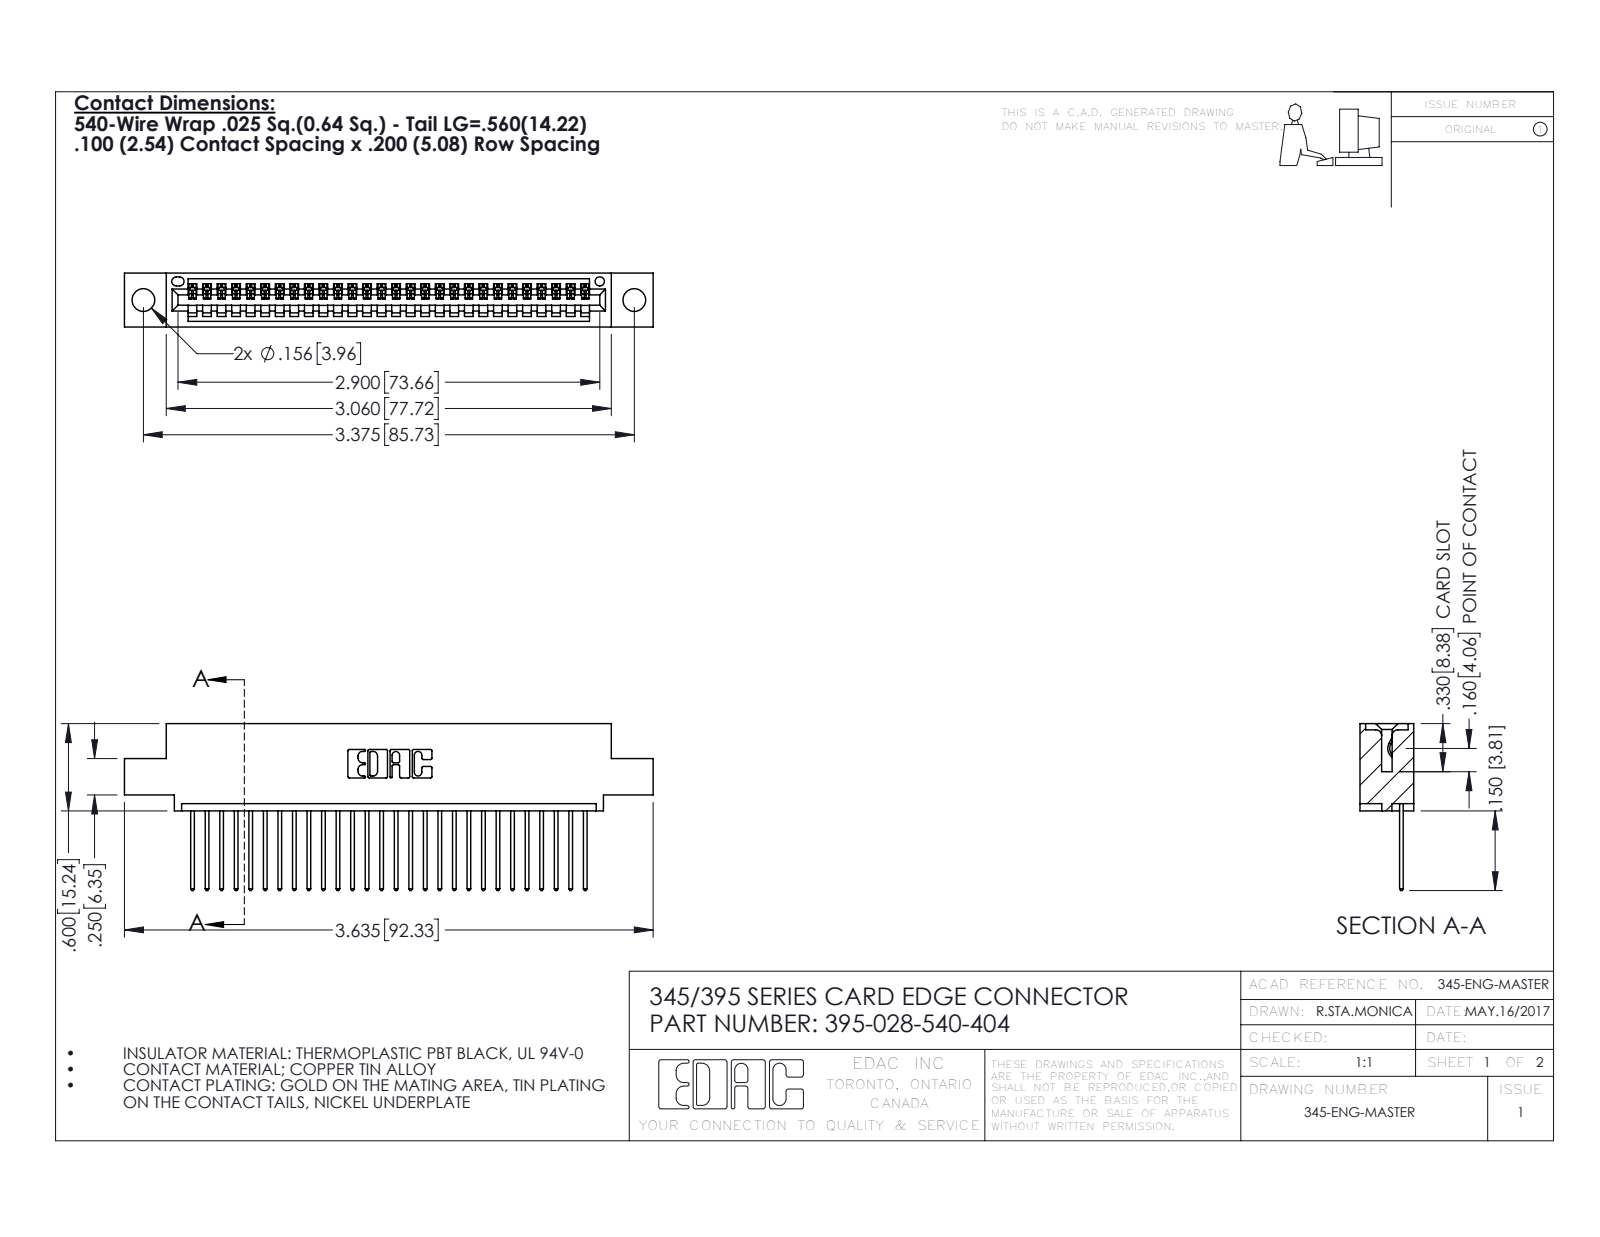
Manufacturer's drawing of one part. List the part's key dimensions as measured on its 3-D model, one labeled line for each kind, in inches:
Part name (STEP PRODUCT): 345 Part_0.110 Offset - 0.156 Dia-TH; 395-028-540-404; 345-292-001_345-293-140
STEP written by: SolidWorks 2016 (CONFIG_CONTROL_DESIGN)
Units: inches
Bodies: 29 solids, 1754 faces (1204 planar, 550 cylindrical, 0 other)
Overall size (bounding box): 3.635 × 1.147 × 0.37
Volume: 0.521 in³ · Surface area: 17.53 in²
Round holes (diameter × count): ⌀0.156 ×2, ⌀0.064 ×1
Partial cylindrical surfaces — rounded edges, fillets, slot ends (radius × count): R0.006 ×56, R0.01 ×56, R0.01 ×22, R0.007 ×6, R0.031 ×6, R0.026 ×3, R0.031 ×2, R0.04 ×2
Main face-to-face distances: 0.298, 0.072, 0.37, 0.2, 0.098, 0.272, 0.025, 0.225, 0.149, 0.072
Hole centre spacings: 0.27, 3.14, 3.375
